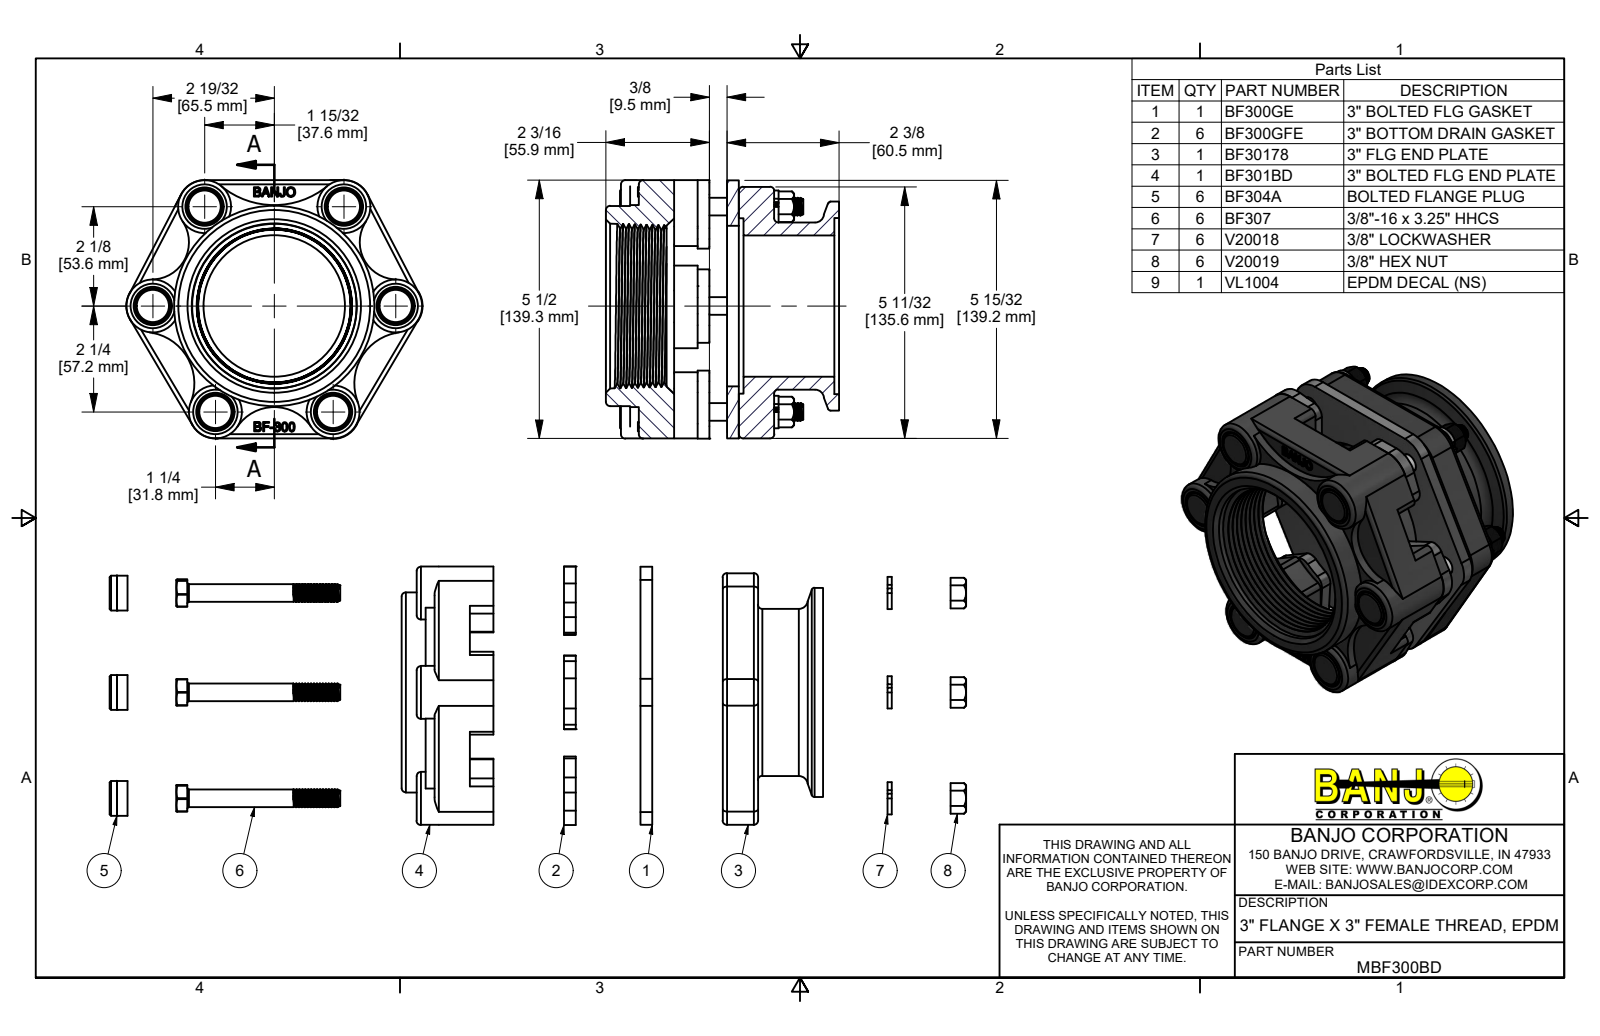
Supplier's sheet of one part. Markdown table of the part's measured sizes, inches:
| quantity | value |
| --- | --- |
| part name | MBF300BD; BF30178; BF301BD; BF304A (+5 more) |
| STEP written by | Autodesk Inventor 2019 (AUTOMOTIVE_DESIGN) |
| units | inches |
| bodies | 33 solids, 1590 faces (505 planar, 529 cylindrical, 556 other) |
| overall size | 6.293 × 5.491 × 4.955 |
| volume | 49.8 in³ |
| surface area | 336.9 in² |
| round holes (diameter × count) | 0.307 × 6, 0.385 × 6, 0.406 × 6, 0.41 × 6, 0.715 × 6, 0.75 × 6, 3 × 1, 3.41 × 1, 3.725 × 1, 3.74 × 1 |
| round bosses / shafts (diameter × count) | 0.324 × 90, 1.125 × 6, 0.742 × 6, 0.687 × 6, 0.375 × 6, 4.44 × 1, 4.25 × 1, 3.55 × 1 |
| partial cylindrical surfaces (radius × count) | 0.125 × 24, 0.25 × 24, 0.09 × 18, 0.162 × 12, 0.562 × 12, 0.32 × 6, 0.56 × 6, 1.71 × 6 |
| main face-to-face distances | 0.25, 0.625, 0.75, 1.375, 0.875, 1.625, 1, 2.125, 0.375, 0.1 |
| hole center spacings | 2.38, 2.574, 2.577, 2.58, 2.614, 4.366, 4.442, 4.575 |
